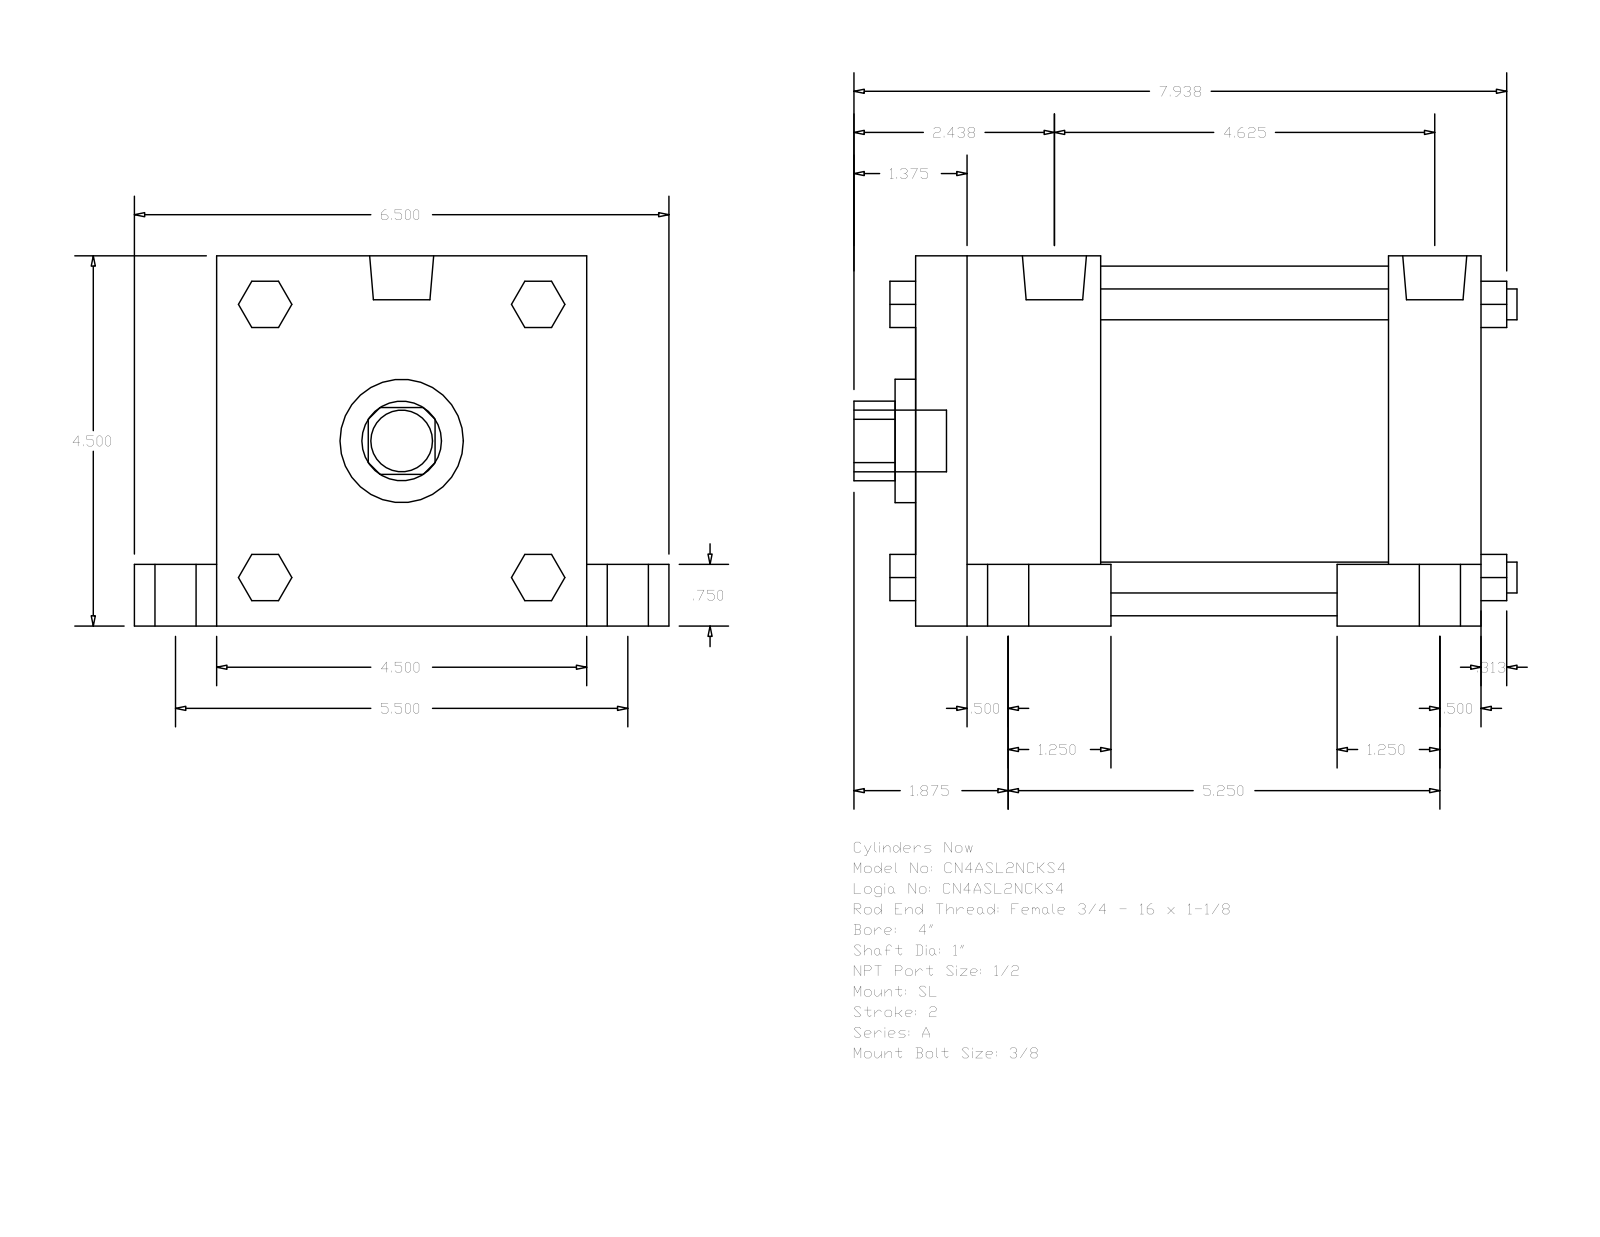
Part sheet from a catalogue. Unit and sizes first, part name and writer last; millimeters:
Units: millimetres
Overall size (bounding box): 204.79 × 165.1 × 114.3
Round holes (diameter × count): ⌀25.4 ×1, ⌀38.1 ×1, ⌀107.95 ×1
Round bosses / shafts (diameter × count): ⌀19.05 ×5, ⌀12.7 ×4, ⌀9.53 ×4, ⌀8.73 ×4, ⌀19.77 ×2
Partial cylindrical surfaces — rounded edges, fillets, slot ends (radius × count): R12.29 ×1
Main face-to-face distances: 114.3, 174.63, 57.15, 117.48, 146.05, 88.9, 28.58, 19.05, 25.4, 139.7
Bodies: 0 solids, 150 faces (114 planar, 36 cylindrical, 0 other)
Part name (STEP PRODUCT): A_SL__0400_1
STEP written by: GSSL Pune (CONFIG_CONTROL_DESIGN)
